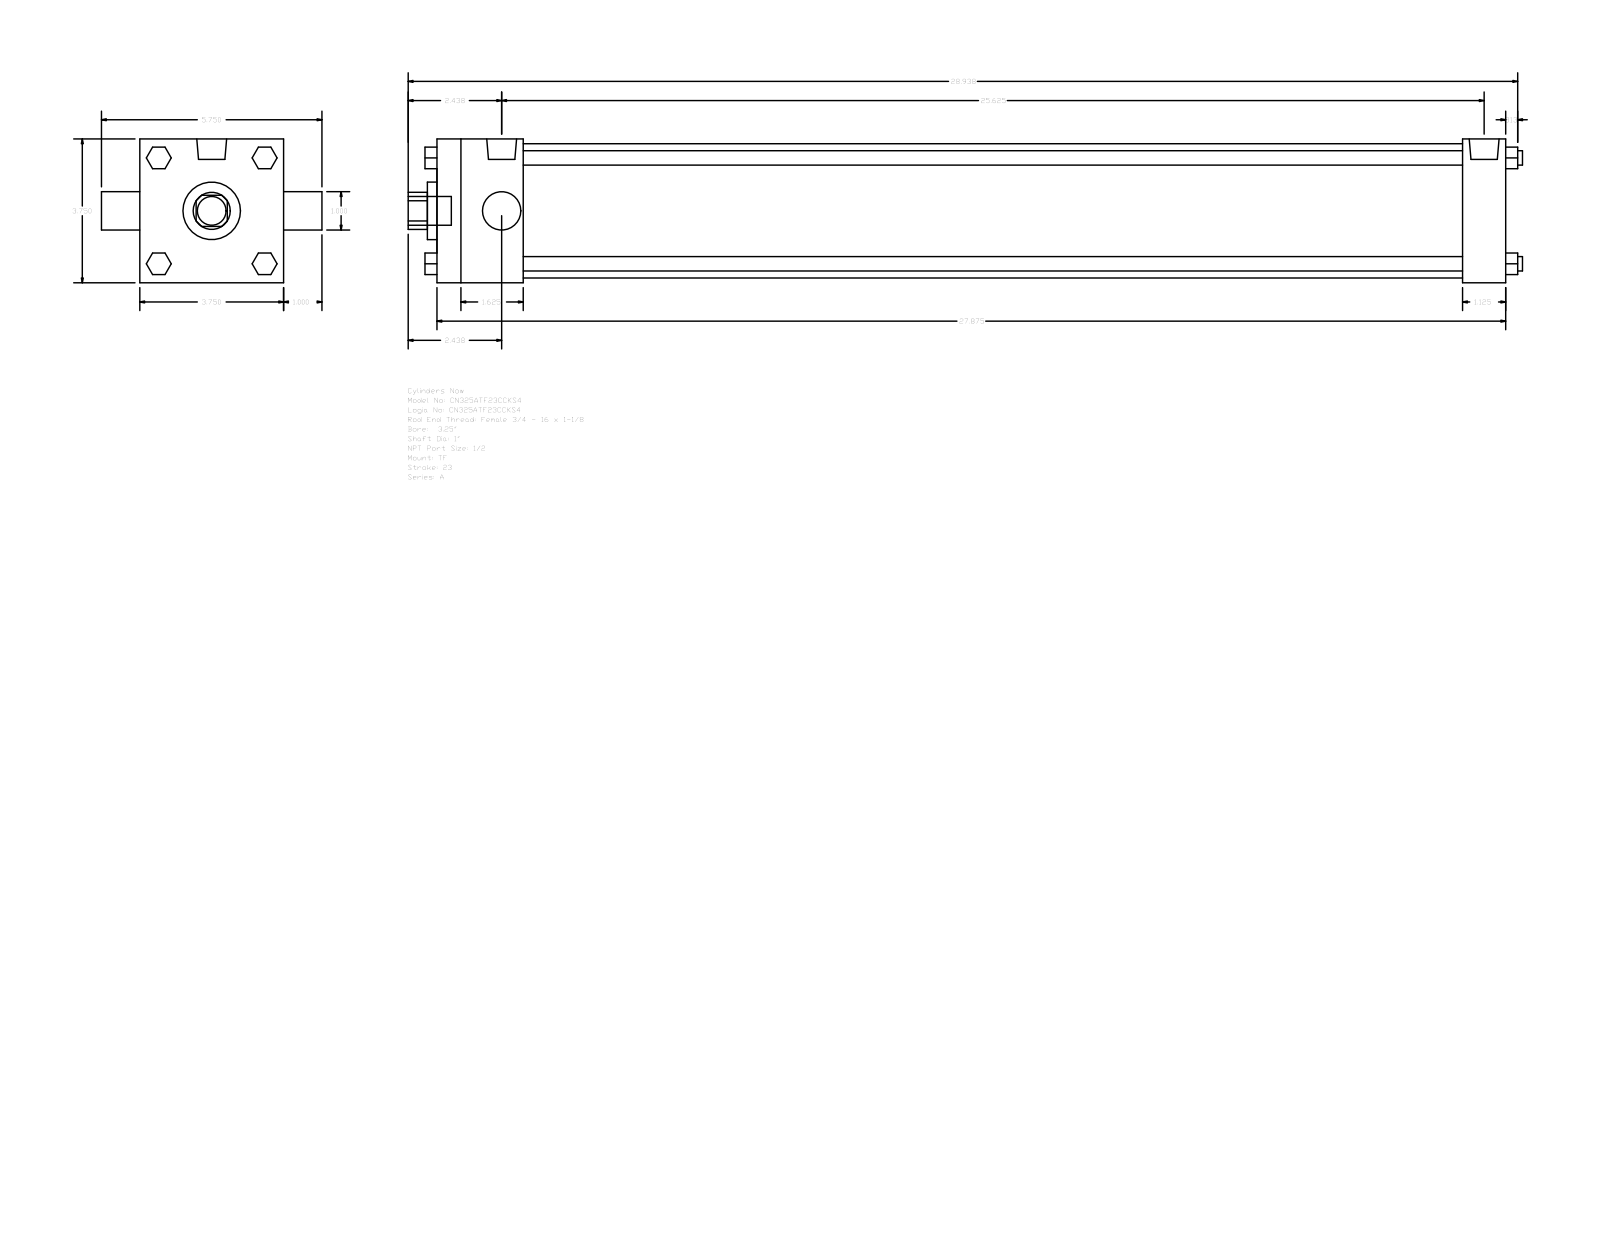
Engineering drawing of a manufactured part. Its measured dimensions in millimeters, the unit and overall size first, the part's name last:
Units: millimetres
Overall size (bounding box): 738.19 × 146.05 × 95.25
Round holes (diameter × count): ⌀25.4 ×2, ⌀38.1 ×1, ⌀88.9 ×1
Round bosses / shafts (diameter × count): ⌀9.53 ×4, ⌀8.73 ×3, ⌀19.77 ×2, ⌀19.05 ×1
Partial cylindrical surfaces — rounded edges, fillets, slot ends (radius × count): R12.29 ×1
Main face-to-face distances: 95.24, 708.03, 57.15, 679.45, 622.3, 650.88, 28.58, 14.28, 35.05, 60.71
Bodies: 0 solids, 120 faces (92 planar, 28 cylindrical, 0 other)
Part name (STEP PRODUCT): A_TF__0325_1
STEP written by: GSSL Pune (CONFIG_CONTROL_DESIGN)
